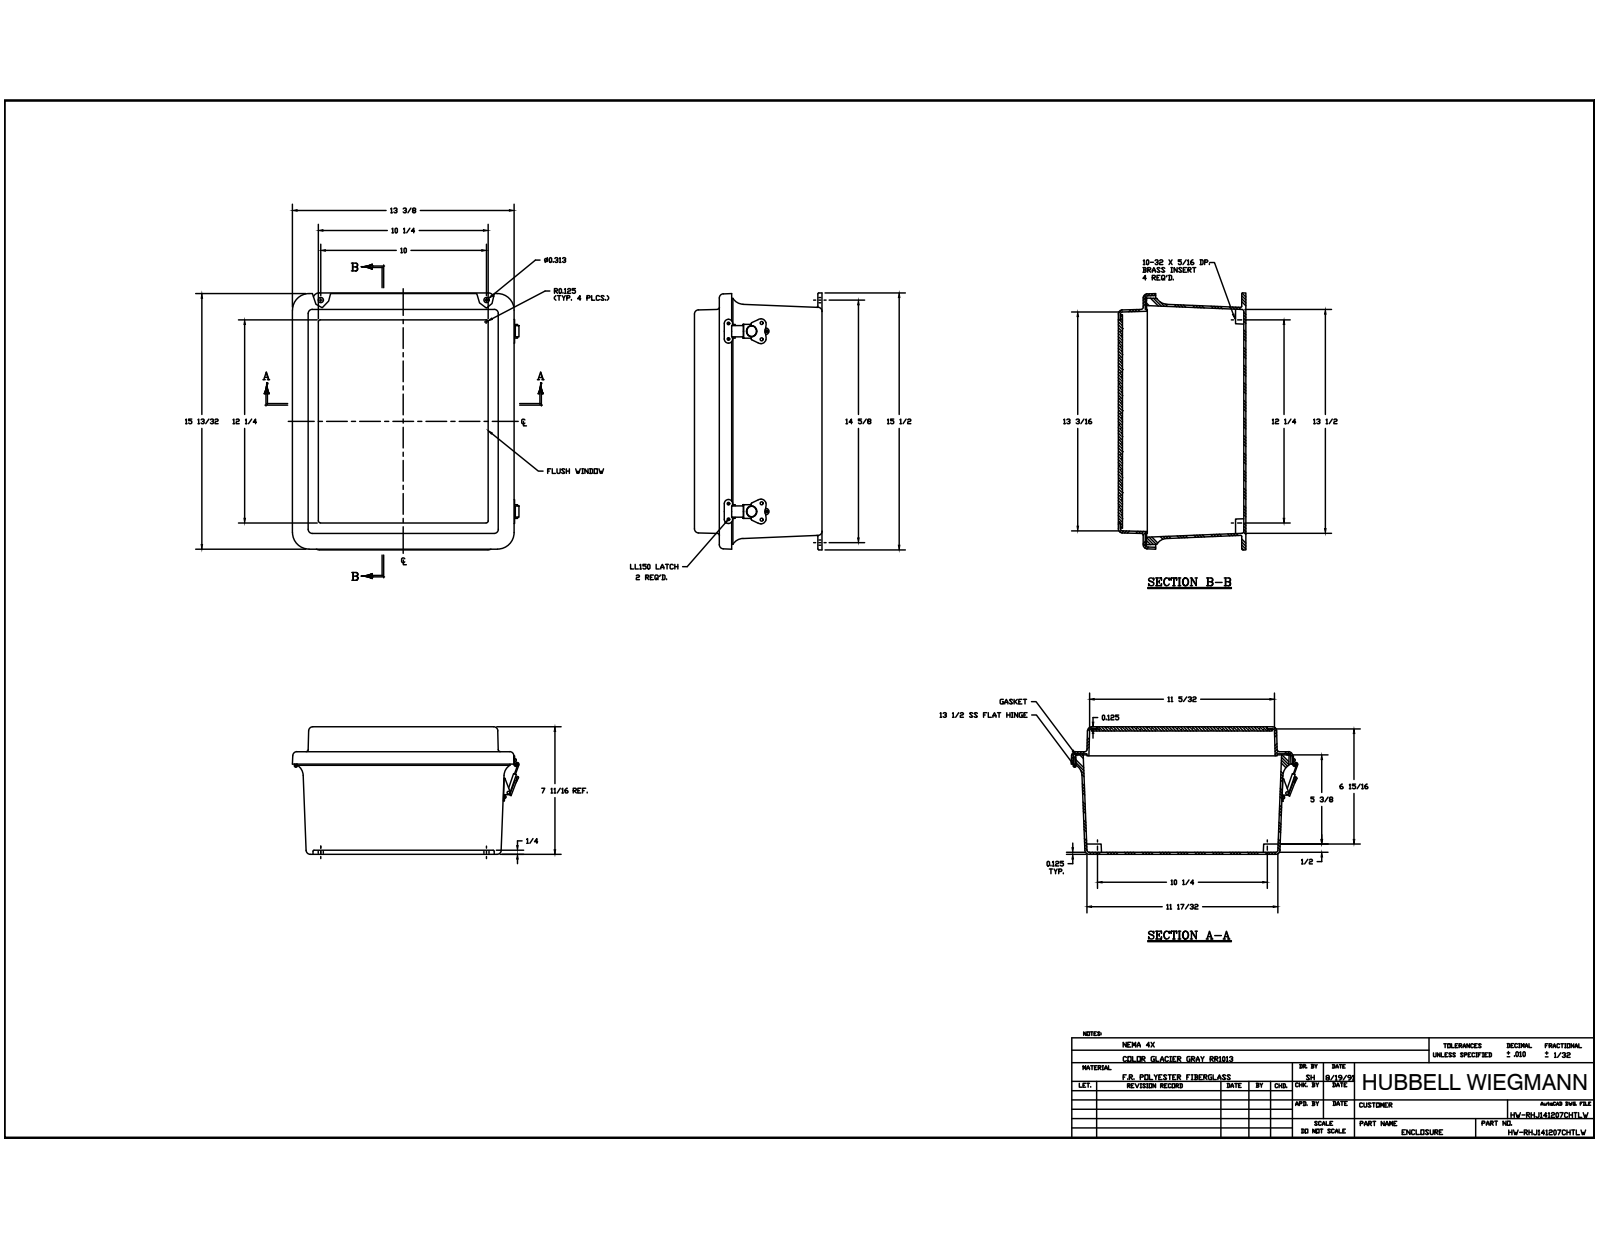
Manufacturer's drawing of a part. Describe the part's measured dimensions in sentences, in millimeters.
The part is named "J1412HL_7; RMINS45821P_311; RMINS45821P_312; RMINS45821P_313 (+8 more)". Its 3-D file was written by "Autodesk Inventor 2014 (AUTOMOTIVE_DESIGN)". It is 51 solids with 1306 faces: 585 planar, 504 cylindrical and 217 other. Overall it measures 393.7 by 344.94 by 195.65 millimeters. Its volume is 2 244 000 cubic millimeters and its surface area 1 153 000 square millimeters. Round holes: 18 of diameter 3.56, 10 of diameter 3.33, 8 of diameter 3.86, 4 of diameter 3.3, 4 of diameter 3.96, 4 of diameter 4.2, 4 of diameter 5, 4 of diameter 5.54, 2 of diameter 3, 2 of diameter 3.5, 2 of diameter 4.61, 2 of diameter 4.62. Round bosses or shafts: 18 of diameter 6.35, 18 of diameter 3.17, 4 of diameter 6.86, 2 of diameter 14.8, 2 of diameter 13.3, 2 of diameter 5.3, 2 of diameter 4.7, 2 of diameter 3.25. Partial cylindrical surfaces (rounded edges, fillets, slot ends): 24 of radius 3.17, 24 of radius 6.35, 20 of radius 0.79, 19 of radius 2, 8 of radius 0.95, 8 of radius 1, 8 of radius 1.15, 8 of radius 1.2. The main face-to-face distances are 3.18, 189.3, 3.17, 6.35, 195.65, 192.47, 186.12, 151.2, 38.1, 154.38. The hole center spacings are 82.55, 165.1, 276.4, 247.65, 6.35, 76.2, 23.83, 34.8.
